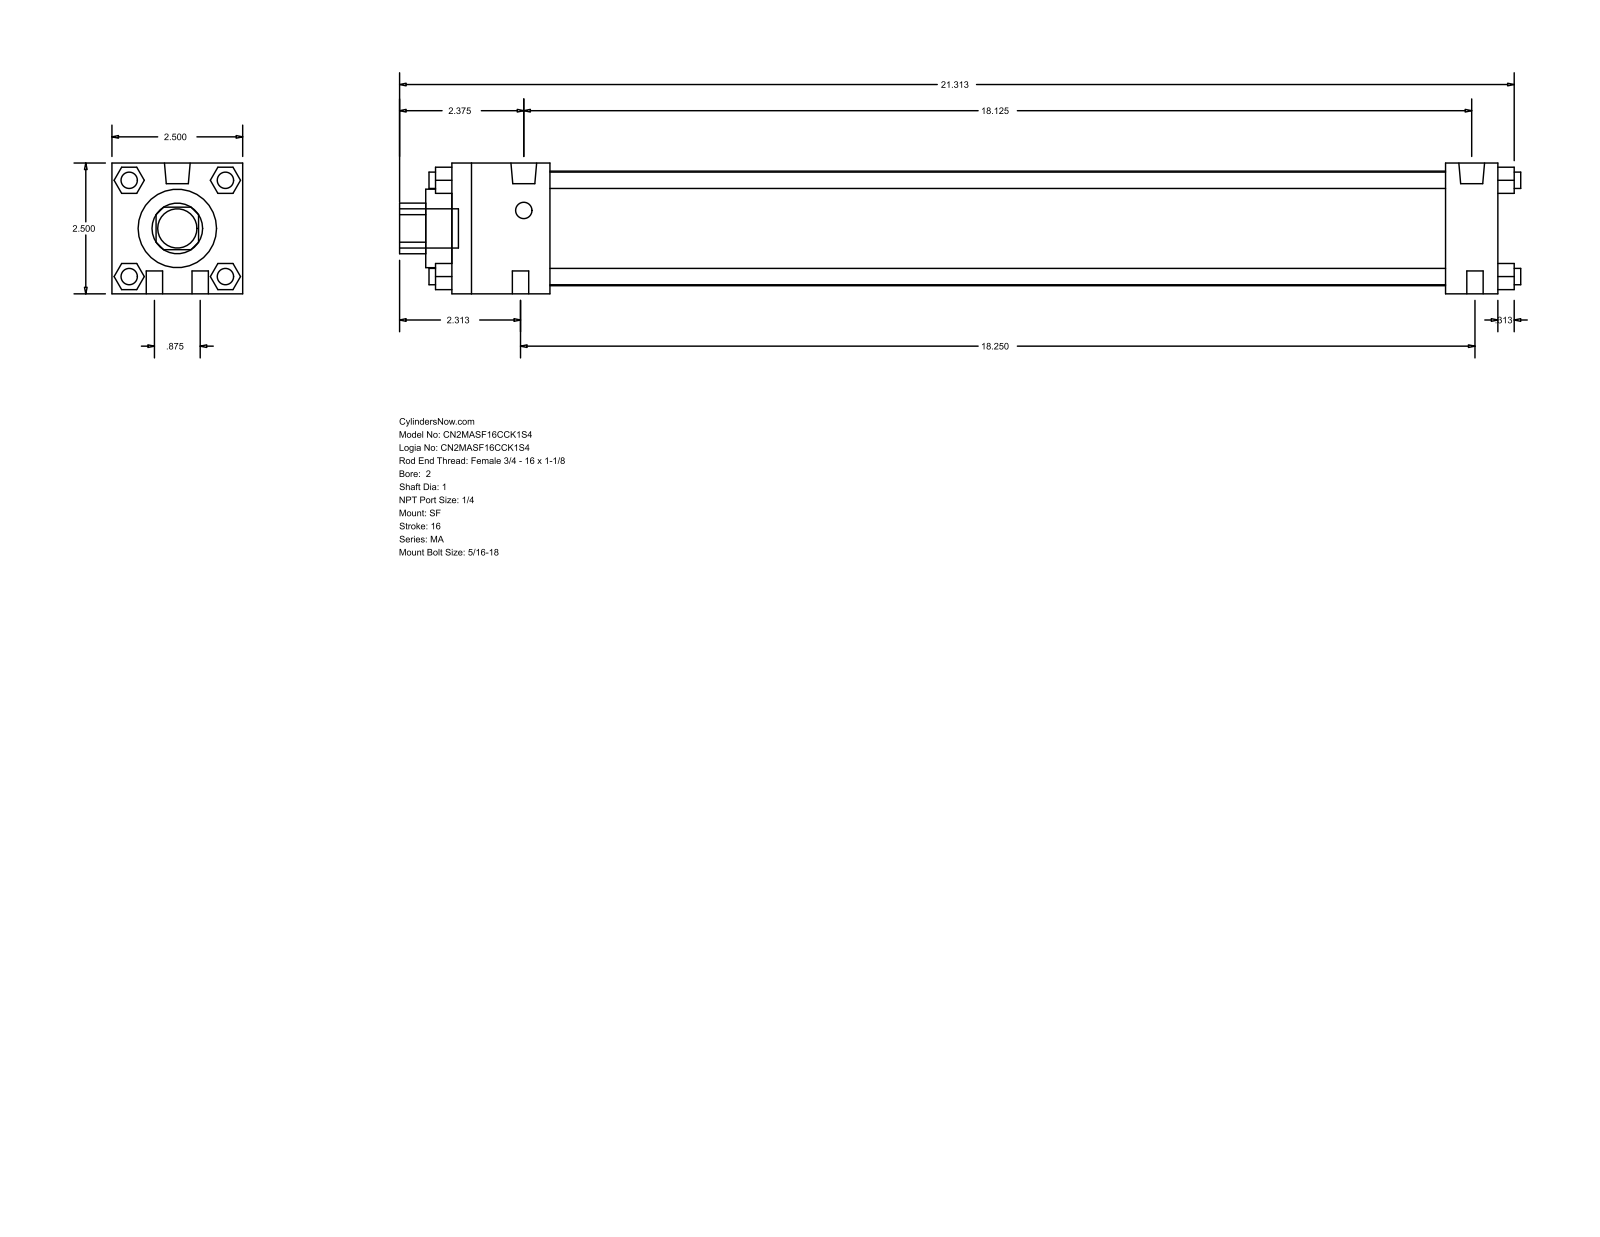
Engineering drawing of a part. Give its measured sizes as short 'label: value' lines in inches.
name: MA_SF__0200_1
written by: GSSL Pune (CONFIG_CONTROL_DESIGN)
unit: in
bodies: 0 solids, 124 faces (94 planar, 30 cylindrical, 0 other)
size: 21.437 × 2.5 × 2.5
holes: 1× ⌀1, 1× ⌀1.5, 1× ⌀2.19
bosses: 10× ⌀0.313, 2× ⌀0.492, 1× ⌀0.75
rounds: 1× R0.484
face distances: 2.5, 20, 0.5, 1, 19, 1.875, 17.125, 18.125, 1.593, 0.92
